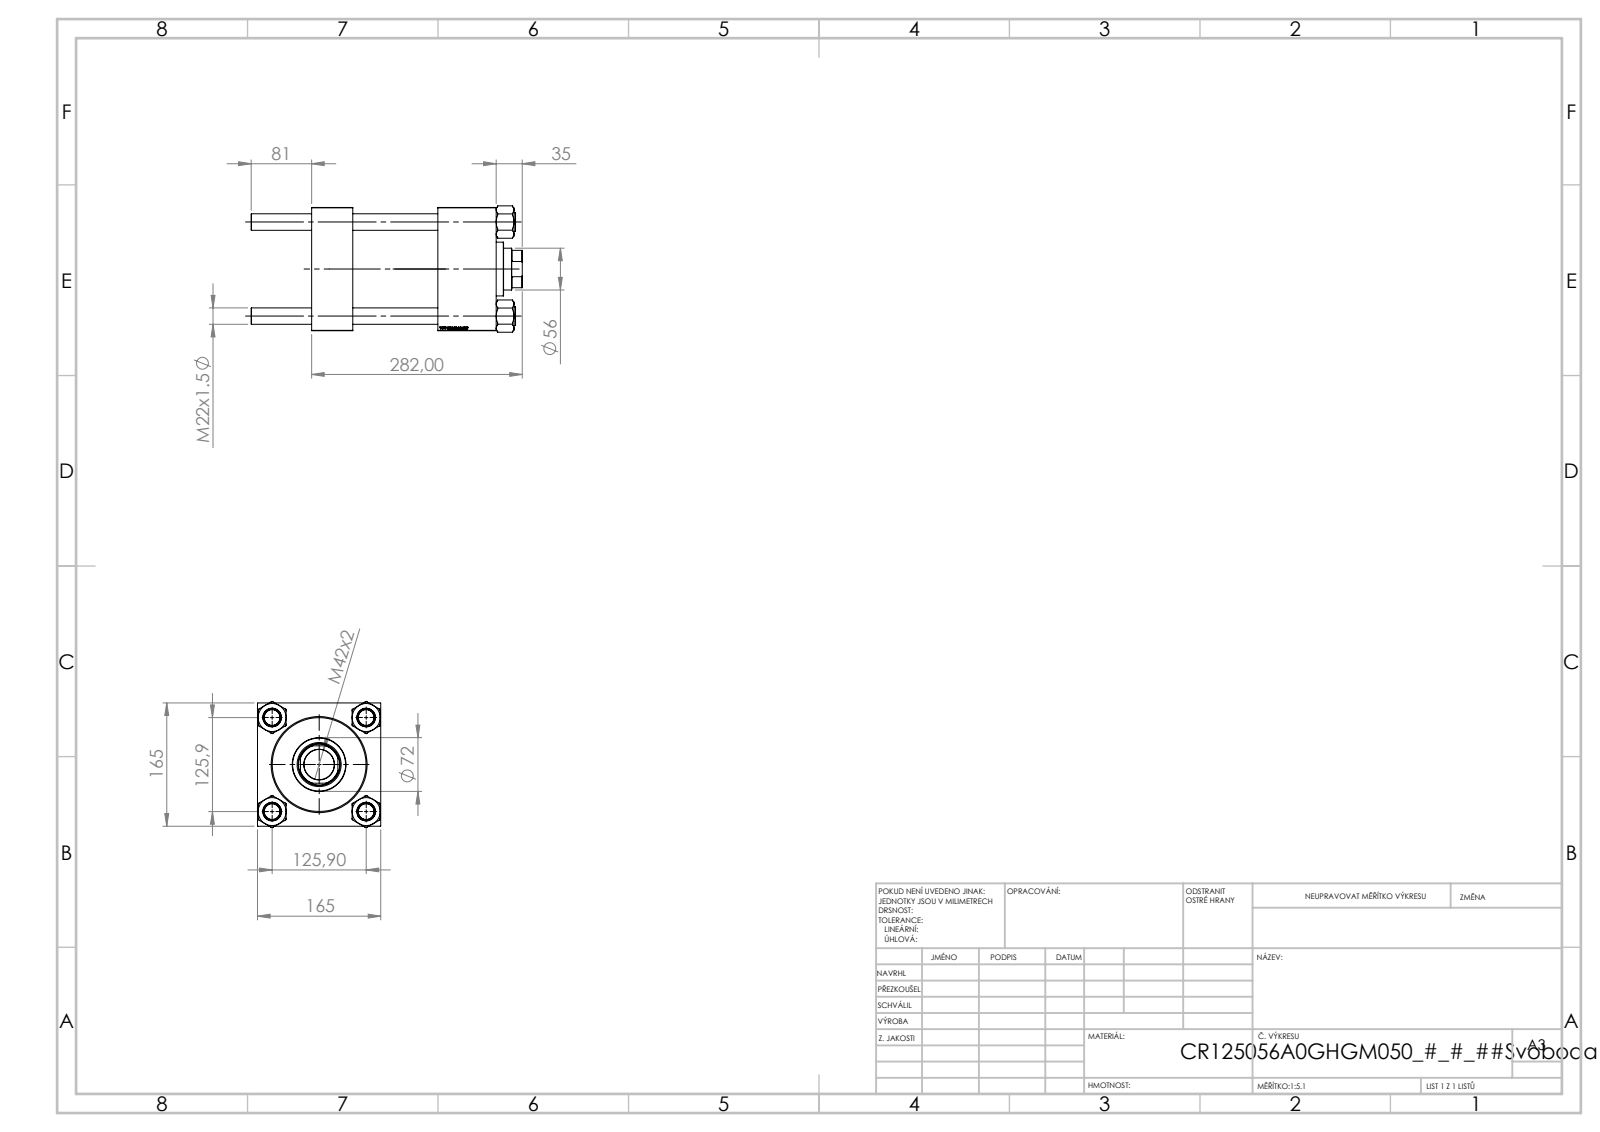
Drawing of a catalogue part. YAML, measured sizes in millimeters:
part_name: "NUT_M5; V215CR_VCP; CR025_012_A_0_G_A_G_M_020_+#_##_TYCINKA; V215CR_BODY_A (+1 more)"
step_written_by: "SolidWorks 2019 (CONFIG_CONTROL_DESIGN)"
units: millimeters
bodies: {solids: 11, faces: 1182, planar: 568, cylindrical: 78, other: 536}
overall_size: [363, 169.14, 165]
volume: 4836000
surface_area: 586348
round_holes:
  - {diameter: 22, count: 4}
  - {diameter: 7, count: 2}
  - {diameter: 32.24, count: 2}
  - {diameter: 45, count: 2}
  - {diameter: 40.5, count: 1}
  - {diameter: 56, count: 1}
  - {diameter: 59, count: 1}
  - {diameter: 96, count: 1}
  - {diameter: 125, count: 1}
  - {diameter: 125.5, count: 1}
round_bosses_or_shafts:
  - {diameter: 25, count: 4}
  - {diameter: 131, count: 1}
  - {diameter: 72, count: 1}
partial_cylinders:
  - {radius: 27, count: 1}
face_to_face_distances: [165, 55, 247, 192, 114, 169, 78, 163.3, 218.3, 49.3]
hole_center_spacings: [89.02, 125.9, 178.05, 168.5]
